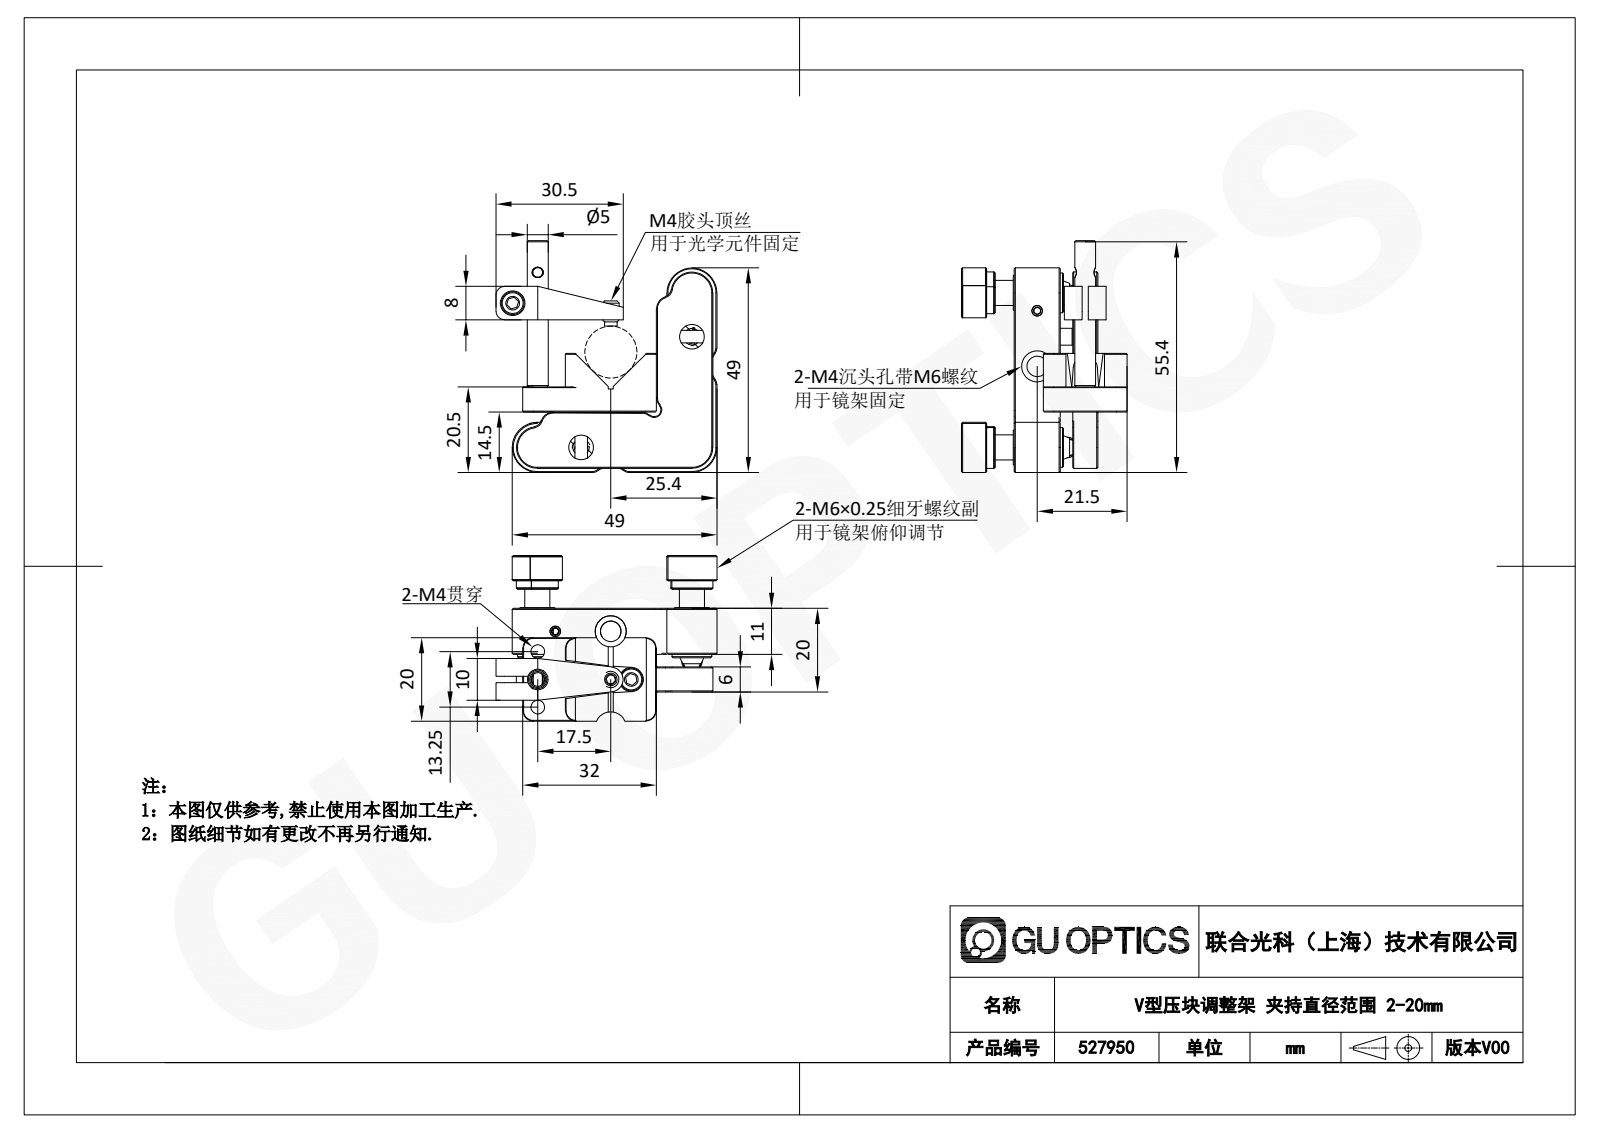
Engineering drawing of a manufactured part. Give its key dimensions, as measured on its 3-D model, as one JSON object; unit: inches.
{"part_name": "2.1.7.1，CVA-20.8，V形调整镜架，范围2-20.8mm，2轴调节", "step_written_by": "SolidWorks 2023 (CONFIG_CONTROL_DESIGN)", "units": "inches", "bodies": {"solids": 0, "faces": 1129, "planar": 455, "cylindrical": 382, "other": 292}, "overall_size": [2.185, 2.083, 1.701], "round_holes": [[0.13, 5], [0.236, 5], [0.081, 4], [0.098, 4], [0.08, 2], [0.157, 2], [0.197, 2], [0.217, 2], [0.256, 2], [0.315, 2], [0.343, 2], [0.386, 2]], "round_bosses_or_shafts": [[0.394, 2], [0.339, 2], [0.236, 2], [0.118, 2], [0.079, 2], [0.059, 2], [0.374, 1], [0.197, 1]], "partial_cylinders_radius": [[0.012, 31], [0.02, 22], [0.079, 8], [0.098, 6], [0.118, 5], [0.031, 4], [0.04, 4], [0.041, 4]], "face_to_face_distances": [0.236, 0.433, 0.591, 0.827, 0.157, 0.394, 0.571, 0.098, 0.472, 0.315], "hole_center_spacings": [0.197, 0.262, 0.295, 0.315, 0.35, 0.382, 0.492, 0.493]}
